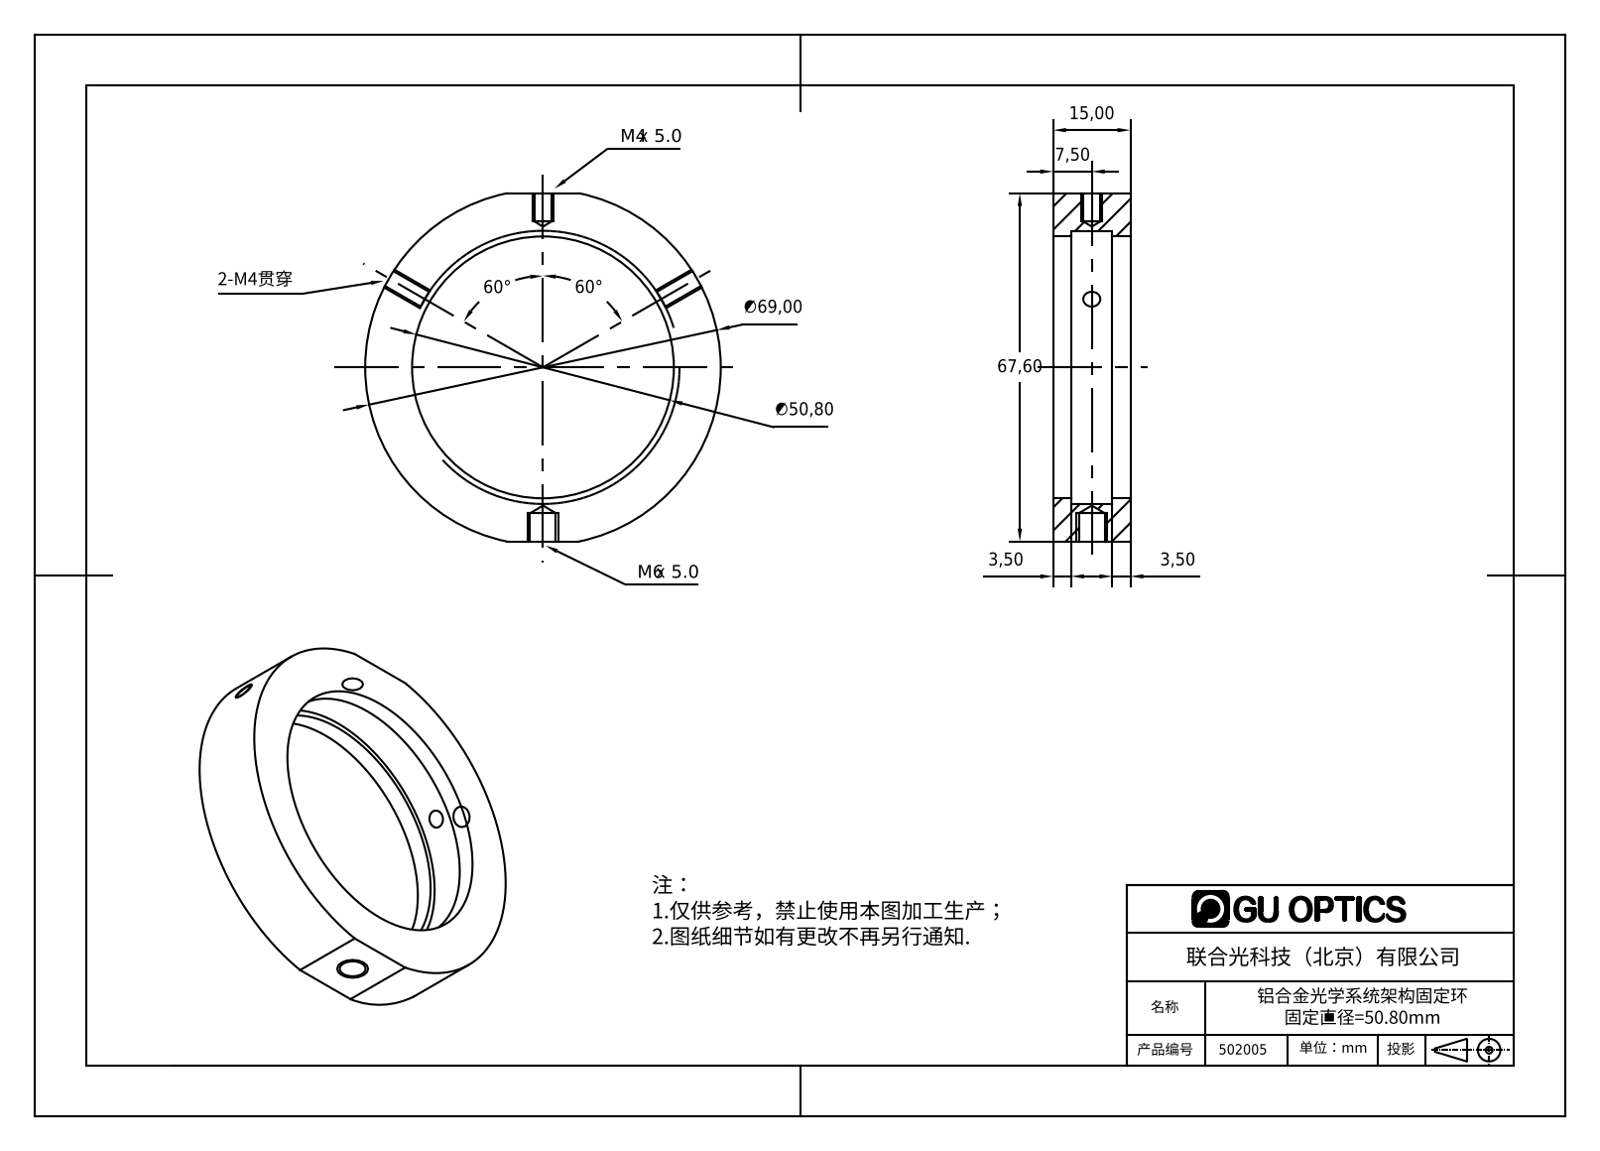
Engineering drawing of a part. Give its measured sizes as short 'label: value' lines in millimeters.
name: 502005
written by: SolidWorks 2016 (CONFIG_CONTROL_DESIGN)
unit: mm
bodies: 1 solid, 27 faces (6 planar, 17 cylindrical, 4 other)
size: 69 × 67.6 × 15
volume: 23 753 mm³; area: 9 736 mm²
holes: 3× ⌀3.3, 1× ⌀5, 1× ⌀50.8, 1× ⌀53
bosses: 1× ⌀69
face distances: 15, 3.5, 11.5, 67.6, 8
